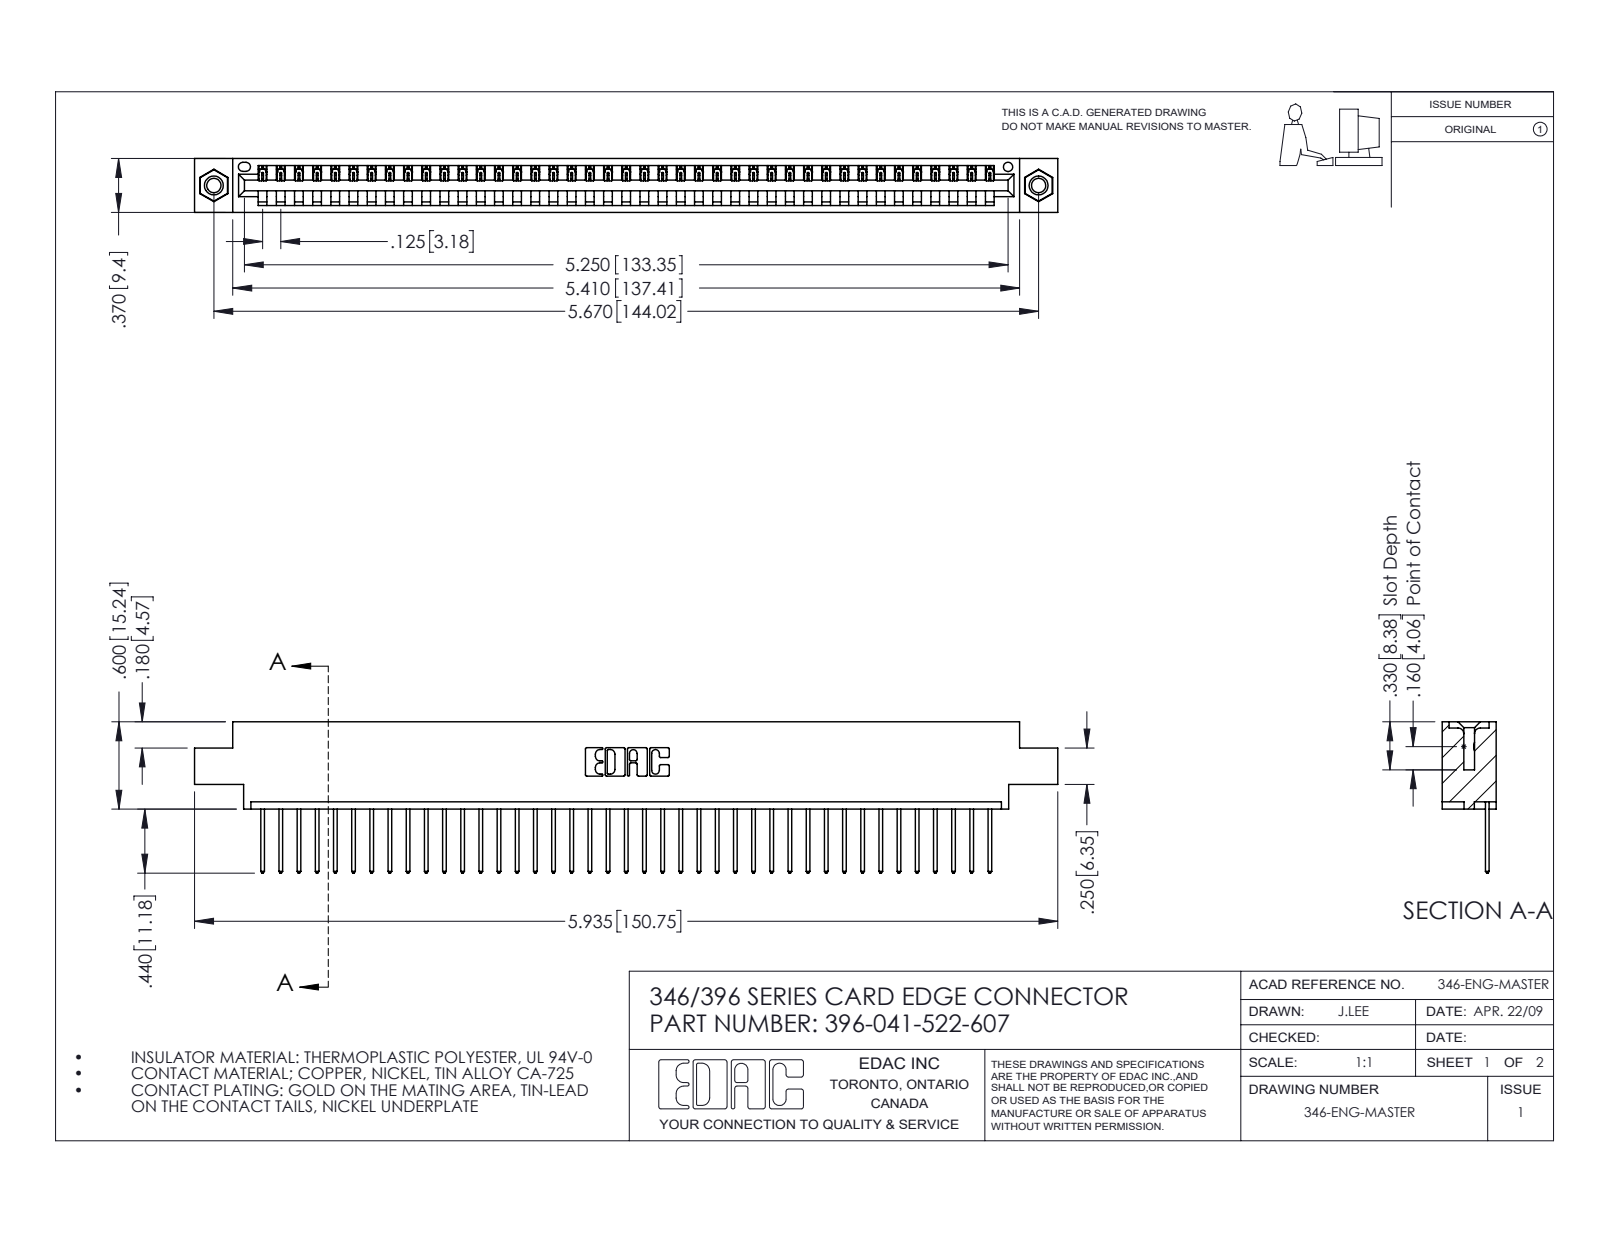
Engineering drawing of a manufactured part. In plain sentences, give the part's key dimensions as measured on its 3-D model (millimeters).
The part is named "345-250-001_345-250-005-103; 346 Part_0.170 Offset - 0.156 Dia-TI; 396-041-522-607; 345-292-001_345-293-122". Its 3-D file was written by "SolidWorks 2016 (CONFIG_CONTROL_DESIGN)". It is 44 solids with 2564 faces: 1752 planar, 796 cylindrical and 16 other. Overall it measures 150.7 by 26.4 by 9.4 millimeters. Its volume is 14 300 cubic millimeters and its surface area 18 160 square millimeters. Round holes: 2 of diameter 2.5, 2 of diameter 3.2, 2 of diameter 4, 1 of diameter 1.6. Round bosses or shafts: 2 of diameter 3.9. Partial cylindrical surfaces (rounded edges, fillets, slot ends): 82 of radius 0.2, 82 of radius 0.3, 22 of radius 0.3, 6 of radius 0.2, 6 of radius 0.8, 3 of radius 0.7, 2 of radius 0.8, 2 of radius 1. The main face-to-face distances are 1.2, 8.2, 9.4, 6.4, 1.8, 7.6, 0.6, 5.6, 3.8, 2.5. The hole center spacings are 6.2, 138.7, 144.
